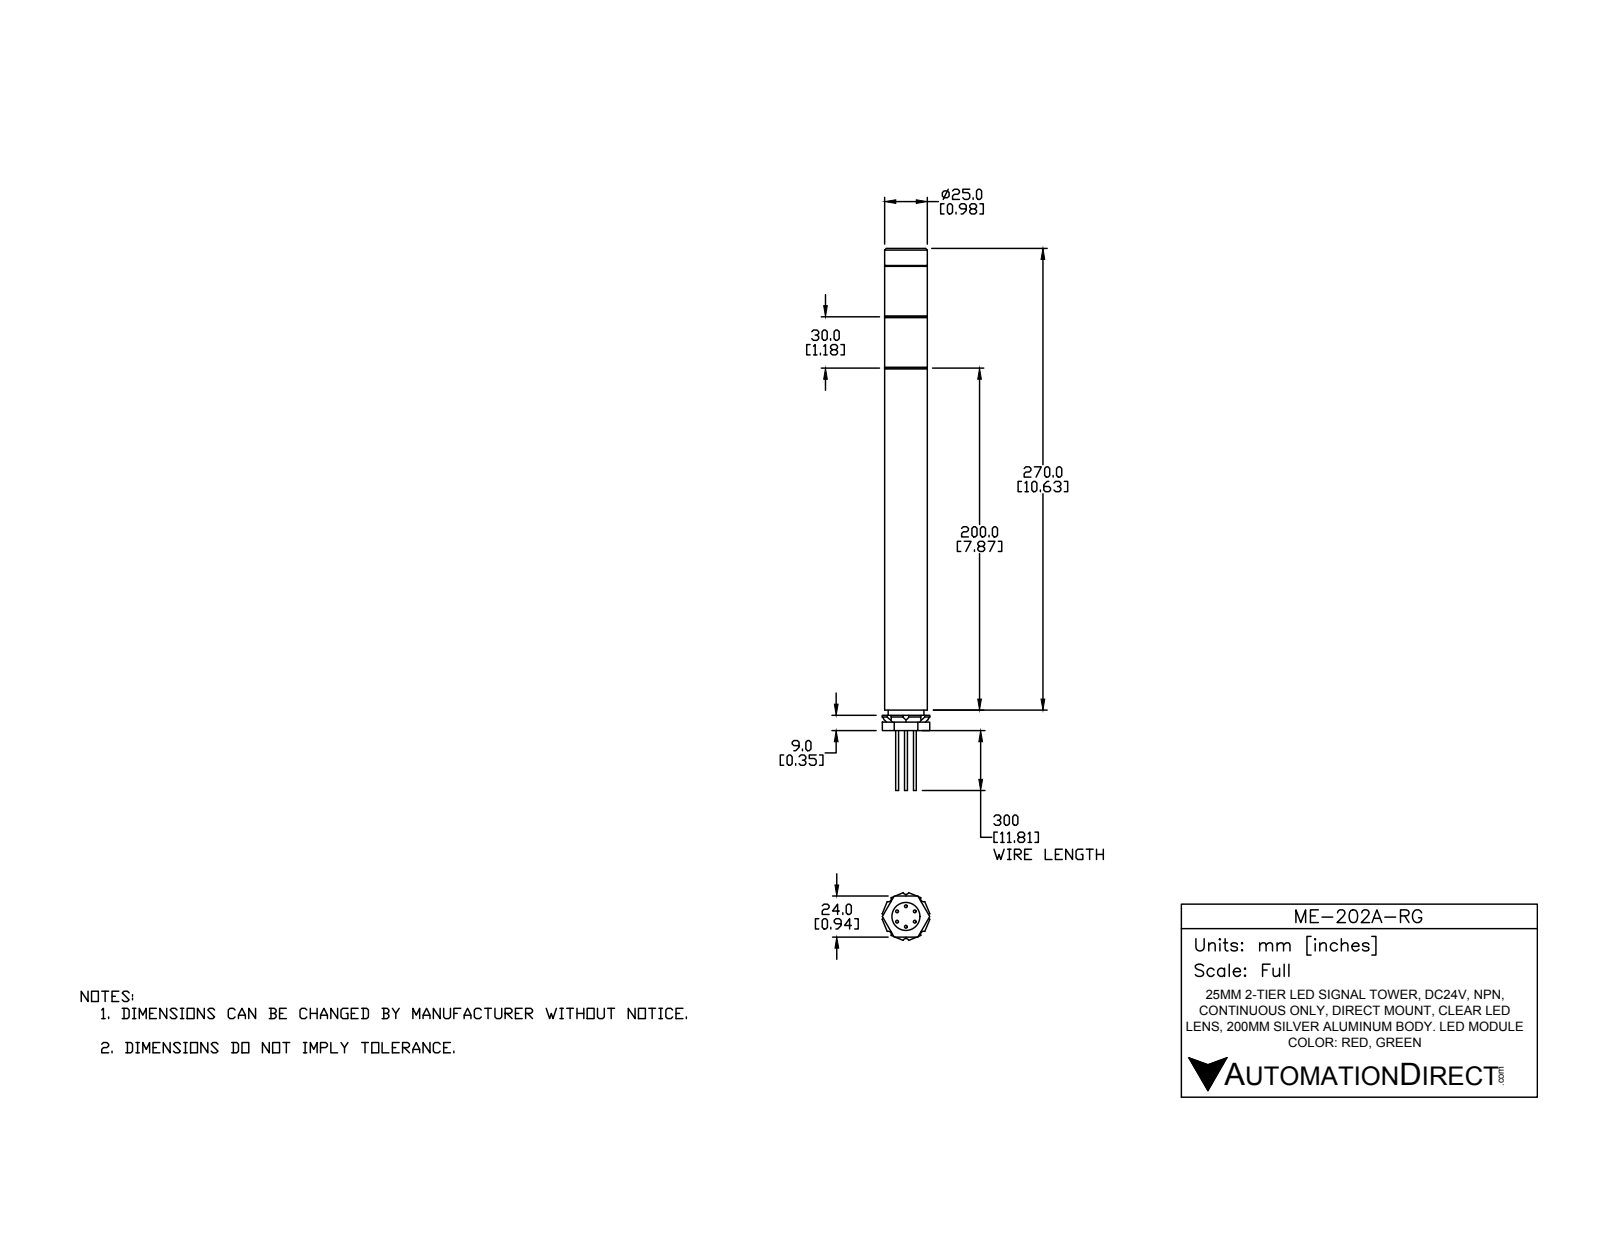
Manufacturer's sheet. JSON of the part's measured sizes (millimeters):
{"part_name": "ME-202A-RG", "step_written_by": "SolidWorks 2016 (AUTOMOTIVE_DESIGN)", "units": "millimeters", "bodies": {"solids": 13, "faces": 140, "planar": 73, "cylindrical": 49, "other": 18}, "overall_size": [317, 27.89, 27.89], "volume_mm3": 126899, "surface_area_mm2": 34535, "round_holes": [[3.2, 1], [7.7, 1], [16.4, 1], [18, 1], [20.7, 1], [21, 1]], "round_bosses_or_shafts": [[1.7, 6], [25, 1], [20.9, 1], [16, 1], [5, 1]], "partial_cylinders_radius": [[1.75, 8]], "face_to_face_distances": [30, 60, 40, 237, 167, 197, 227, 70, 10, 45]}
